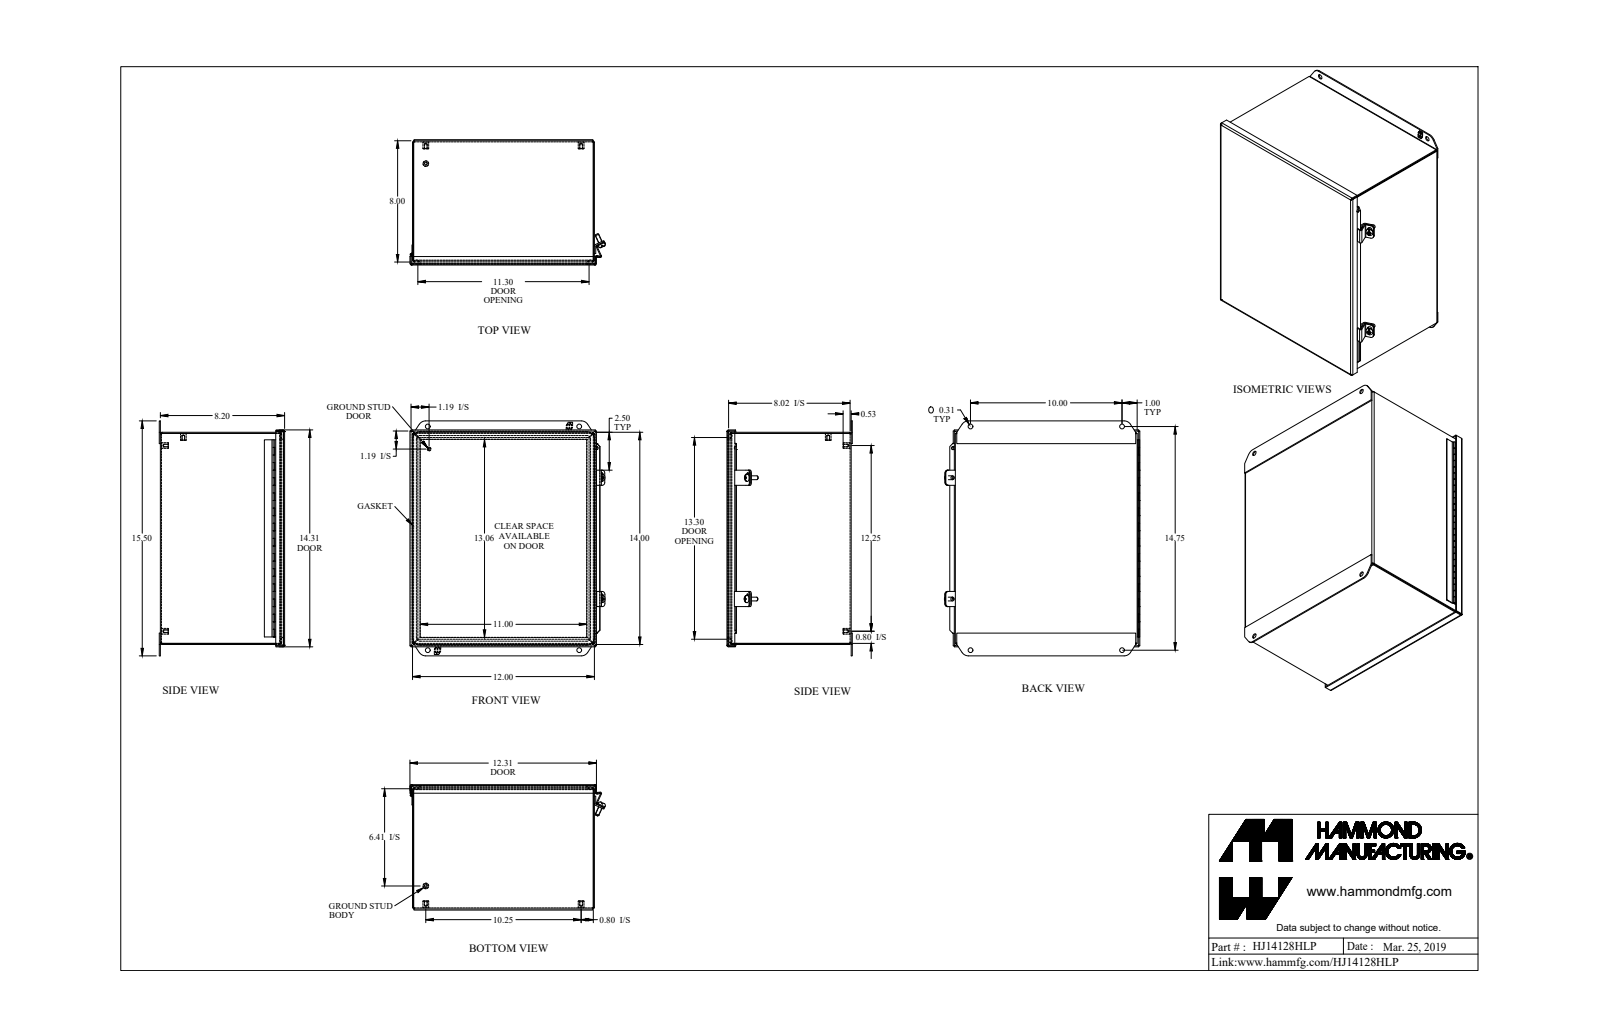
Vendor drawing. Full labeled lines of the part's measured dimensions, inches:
Part name (STEP PRODUCT): HJ14128HLP
STEP written by: SolidWorks 2018 (AUTOMOTIVE_DESIGN)
Units: inches
Bodies: 20 solids, 809 faces (430 planar, 251 cylindrical, 128 other)
Overall size (bounding box): 15.5 × 12.896 × 8.269
Volume: 65.58 in³ · Surface area: 1 839 in²
Round holes (diameter × count): ⌀0.156 ×5, ⌀0.313 ×4, ⌀0.213 ×2, ⌀0.05 ×1
Round bosses / shafts (diameter × count): ⌀0.375 ×5, ⌀0.25 ×3, ⌀0.48 ×2, ⌀0.188 ×1, ⌀0.1 ×1, ⌀0.045 ×1
Partial cylindrical surfaces — rounded edges, fillets, slot ends (radius × count): R0.25 ×16, R0.036 ×13, R0.108 ×13, R0.01 ×4, R0.029 ×4, R0.086 ×4, R0.141 ×4, R0.188 ×4
Main face-to-face distances: 0.072, 8.125, 11.928, 8.197, 13.928, 8.053, 11.856, 12, 14, 13.856
Hole centre spacings: 10.202, 1.256, 1.257, 10, 10.25, 12.25, 13.5, 13.5
